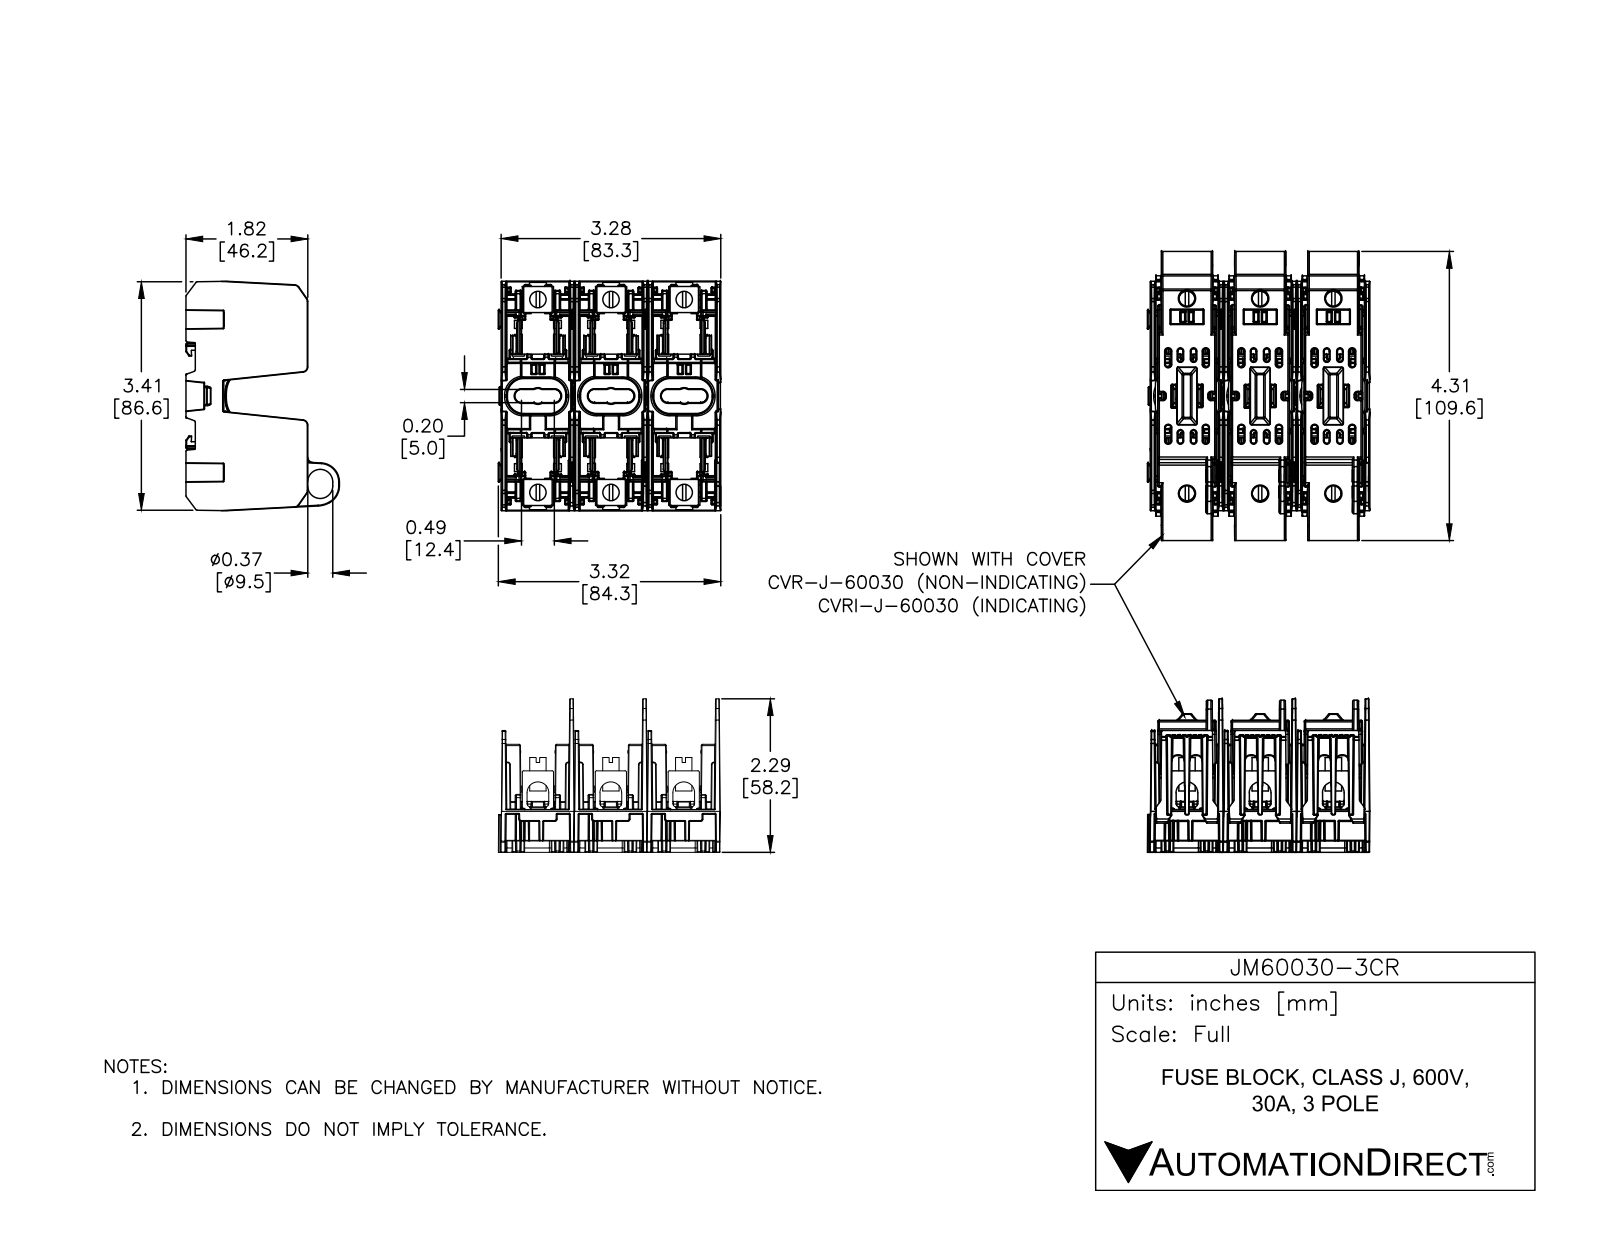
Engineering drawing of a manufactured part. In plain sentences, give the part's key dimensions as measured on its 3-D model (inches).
The part is named "JM60030-1CR; JM60030-3CR". Its 3-D file was written by "SolidWorks 2016 (AUTOMOTIVE_DESIGN)". It is 39 solids with 9279 faces: 2343 planar, 3987 cylindrical and 2949 other. Overall it measures 3.433 by 3.312 by 2.291 inches. Its volume is 5.927 cubic inches and its surface area 154.9 square inches. Round holes: 6 of diameter 0.225, 6 of diameter 0.244. Round bosses or shafts: 6 of diameter 0.244. Partial cylindrical surfaces (rounded edges, fillets, slot ends): 1104 of radius 0.01, 855 of radius 0.006, 119 of radius 0.02, 88 of radius 0.039, 72 of radius 0.004, 24 of radius 0.02, 18 of radius 0.059, 13 of radius 0.079. The main face-to-face distances are 1.089, 1.089, 2.178, 1.013, 0.075, 0.024, 1.014, 2.102, 1.164, 1.164. The hole center spacings are 2.531, 1.089, 1.089, 1.241, 1.241, 2.01, 2.178, 2.257.
